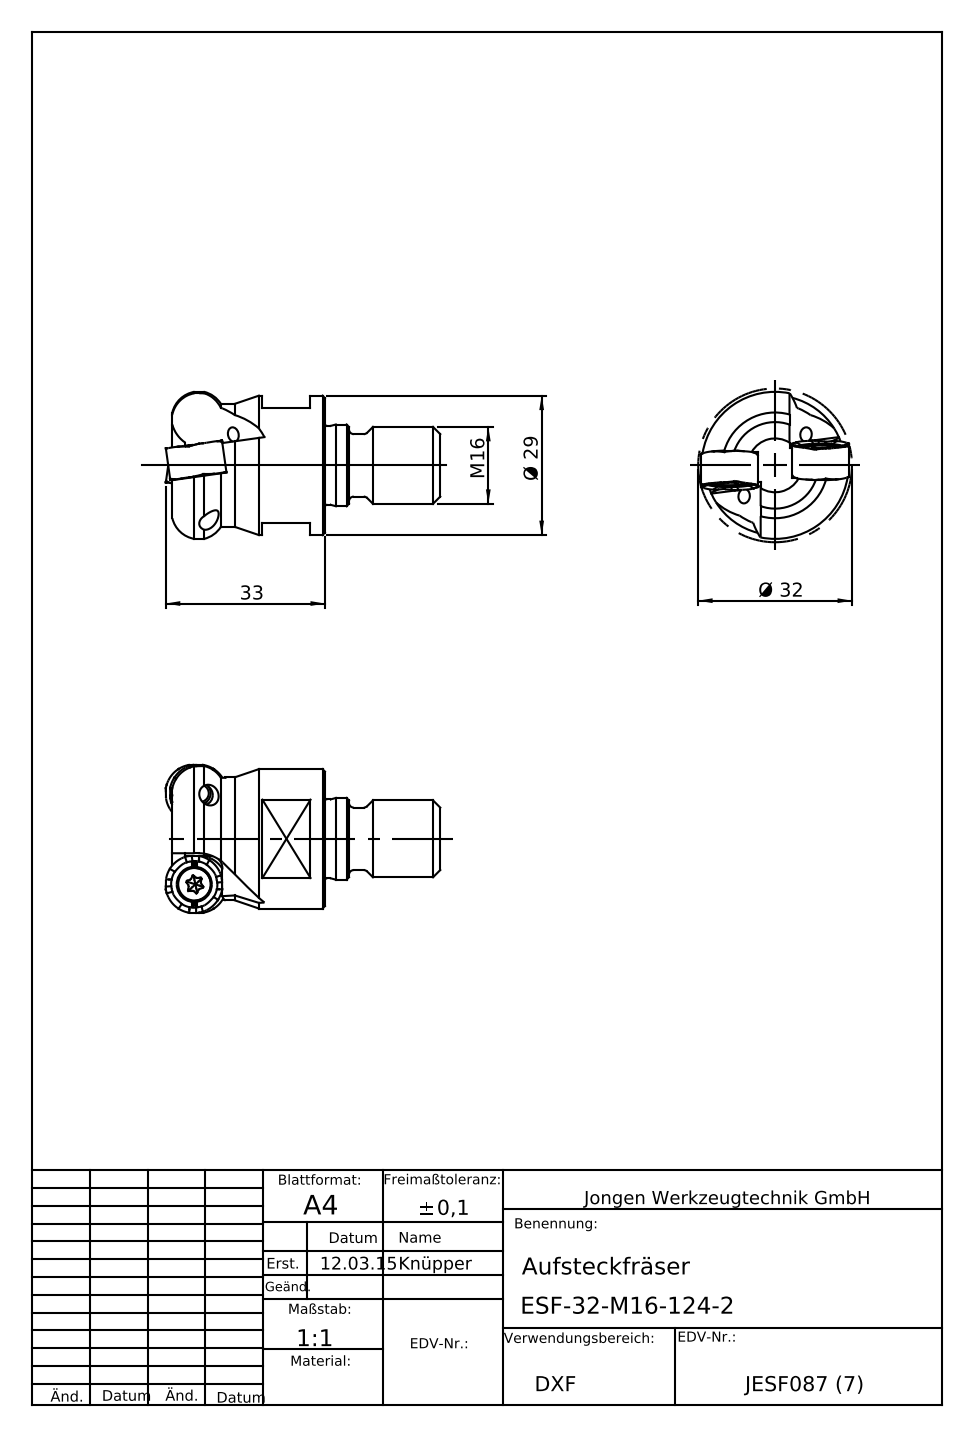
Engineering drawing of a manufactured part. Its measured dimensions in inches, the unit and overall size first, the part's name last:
Units: inches
Overall size (bounding box): 2.243 × 1.258 × 1.258
Round holes (diameter × count): ⌀0.118 ×2, ⌀0.157 ×1
Round bosses / shafts (diameter × count): ⌀1.142 ×1, ⌀1.008 ×1, ⌀0.669 ×1, ⌀0.646 ×1, ⌀0.63 ×1, ⌀0.512 ×1
Partial cylindrical surfaces — rounded edges, fillets, slot ends (radius × count): R0.085 ×2, R0.098 ×2, R0.177 ×2, R0.236 ×2
Main face-to-face distances: 0.945, 1.457, 0.512, 1.063, 0.118, 0.394, 2.089, 1.144, 1.026, 0.632
Volume: 1.469 in³ · Surface area: 10.66 in²
Bodies: 1 solid, 86 faces (24 planar, 29 cylindrical, 33 other)
Part name (STEP PRODUCT): ESF_32_M16_124_2
STEP written by: SolidWorks 2016 (AUTOMOTIVE_DESIGN)
